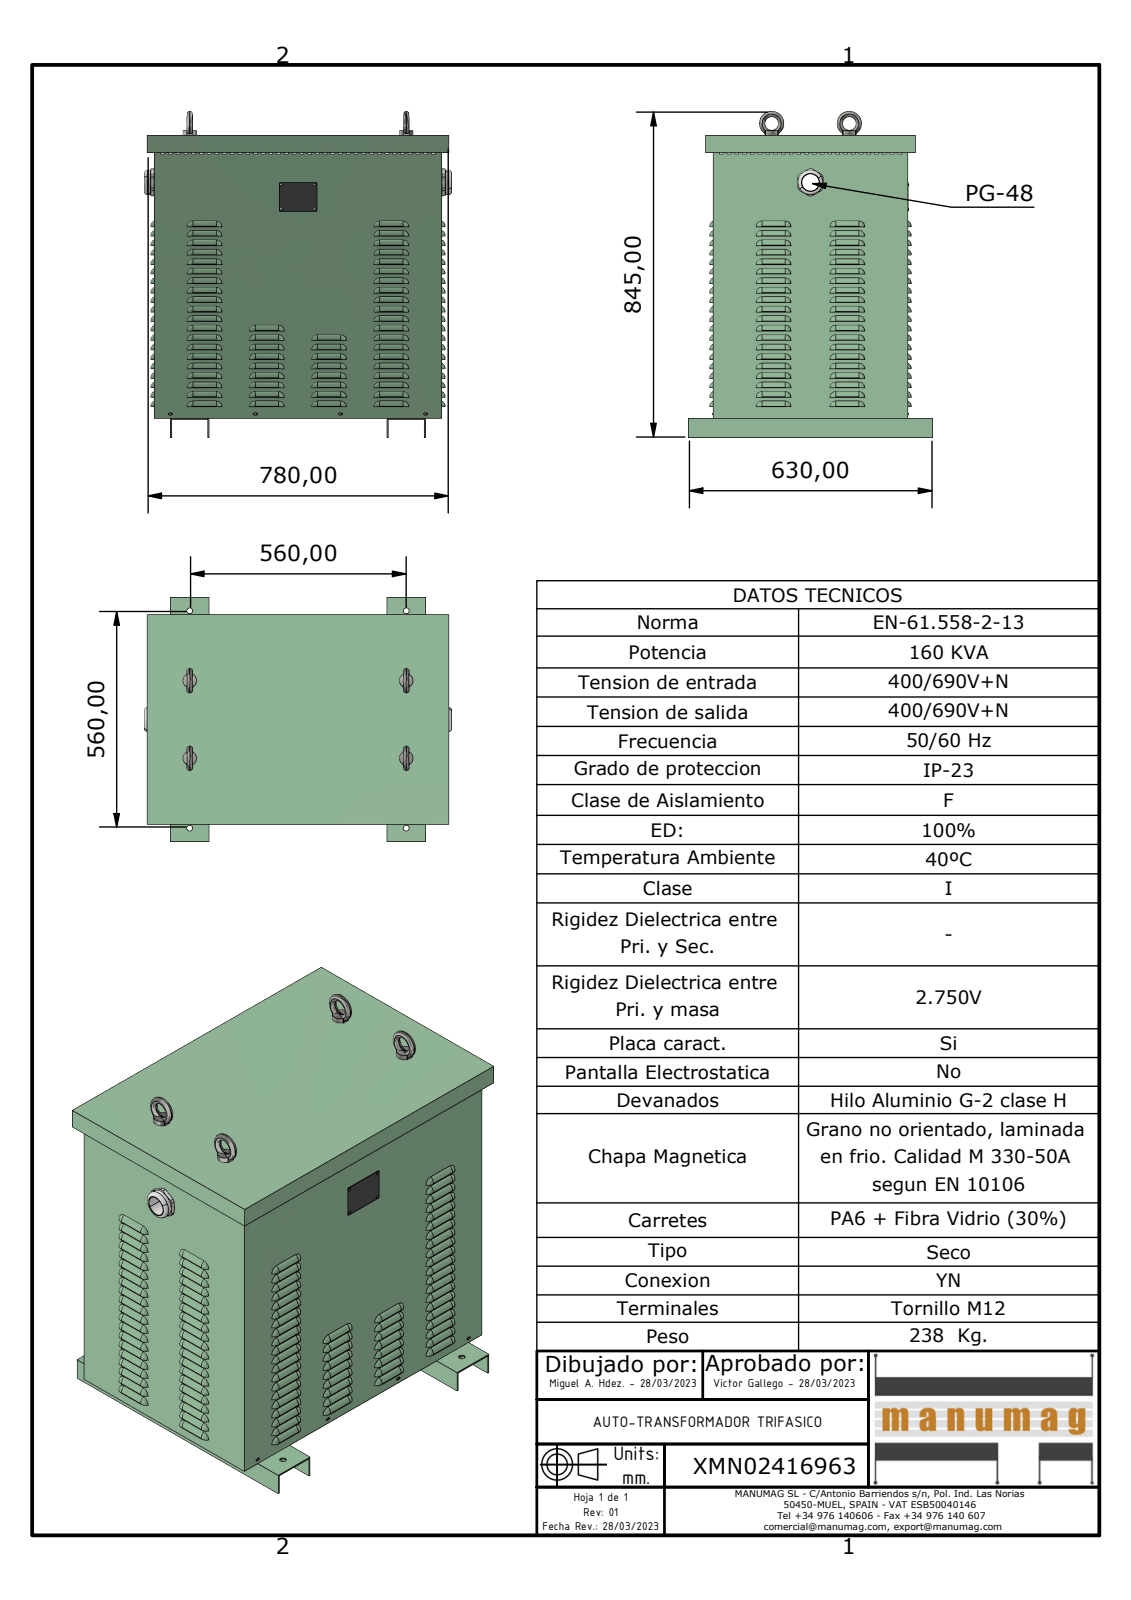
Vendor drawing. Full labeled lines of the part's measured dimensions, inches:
Part name (STEP PRODUCT): XMN02416963; JE160 EXPORT JE200 EXPORT NACIONAL BASE; JE160 EXPORT JE200 EXPORT NACIONAL PATA; JE160 EXPORT CUERPO (+5 more)
STEP written by: Autodesk Inventor 2023 (AUTOMOTIVE_DESIGN)
Units: inches
Bodies: 24 solids, 4187 faces (1441 planar, 1866 cylindrical, 880 other)
Overall size (bounding box): 33.228 × 31.31 × 24.803
Volume: 432.4 in³ · Surface area: 9 697 in²
Round holes (diameter × count): ⌀0.433 ×936, ⌀0.591 ×8, ⌀0.157 ×4, ⌀0.197 ×4, ⌀1.378 ×2, ⌀1.732 ×1, ⌀2.362 ×1
Round bosses / shafts (diameter × count): ⌀0.126 ×8, ⌀0.63 ×4, ⌀0.583 ×4, ⌀2.48 ×3, ⌀2.335 ×1, ⌀2.329 ×1, ⌀2.269 ×1
Partial cylindrical surfaces — rounded edges, fillets, slot ends (radius × count): R0.551 ×194, R0.276 ×84, R0.591 ×80, R0.098 ×8, R0.079 ×4, R0.689 ×4, R1.378 ×1
Main face-to-face distances: 0.079, 19.685, 28.74, 29.213, 19.606, 19.764, 28.819, 29.134, 28.661, 29.291
Hole centre spacings: 0.591, 1.181, 1.32, 8.053, 6.288, 8.031, 5.113, 6.26
